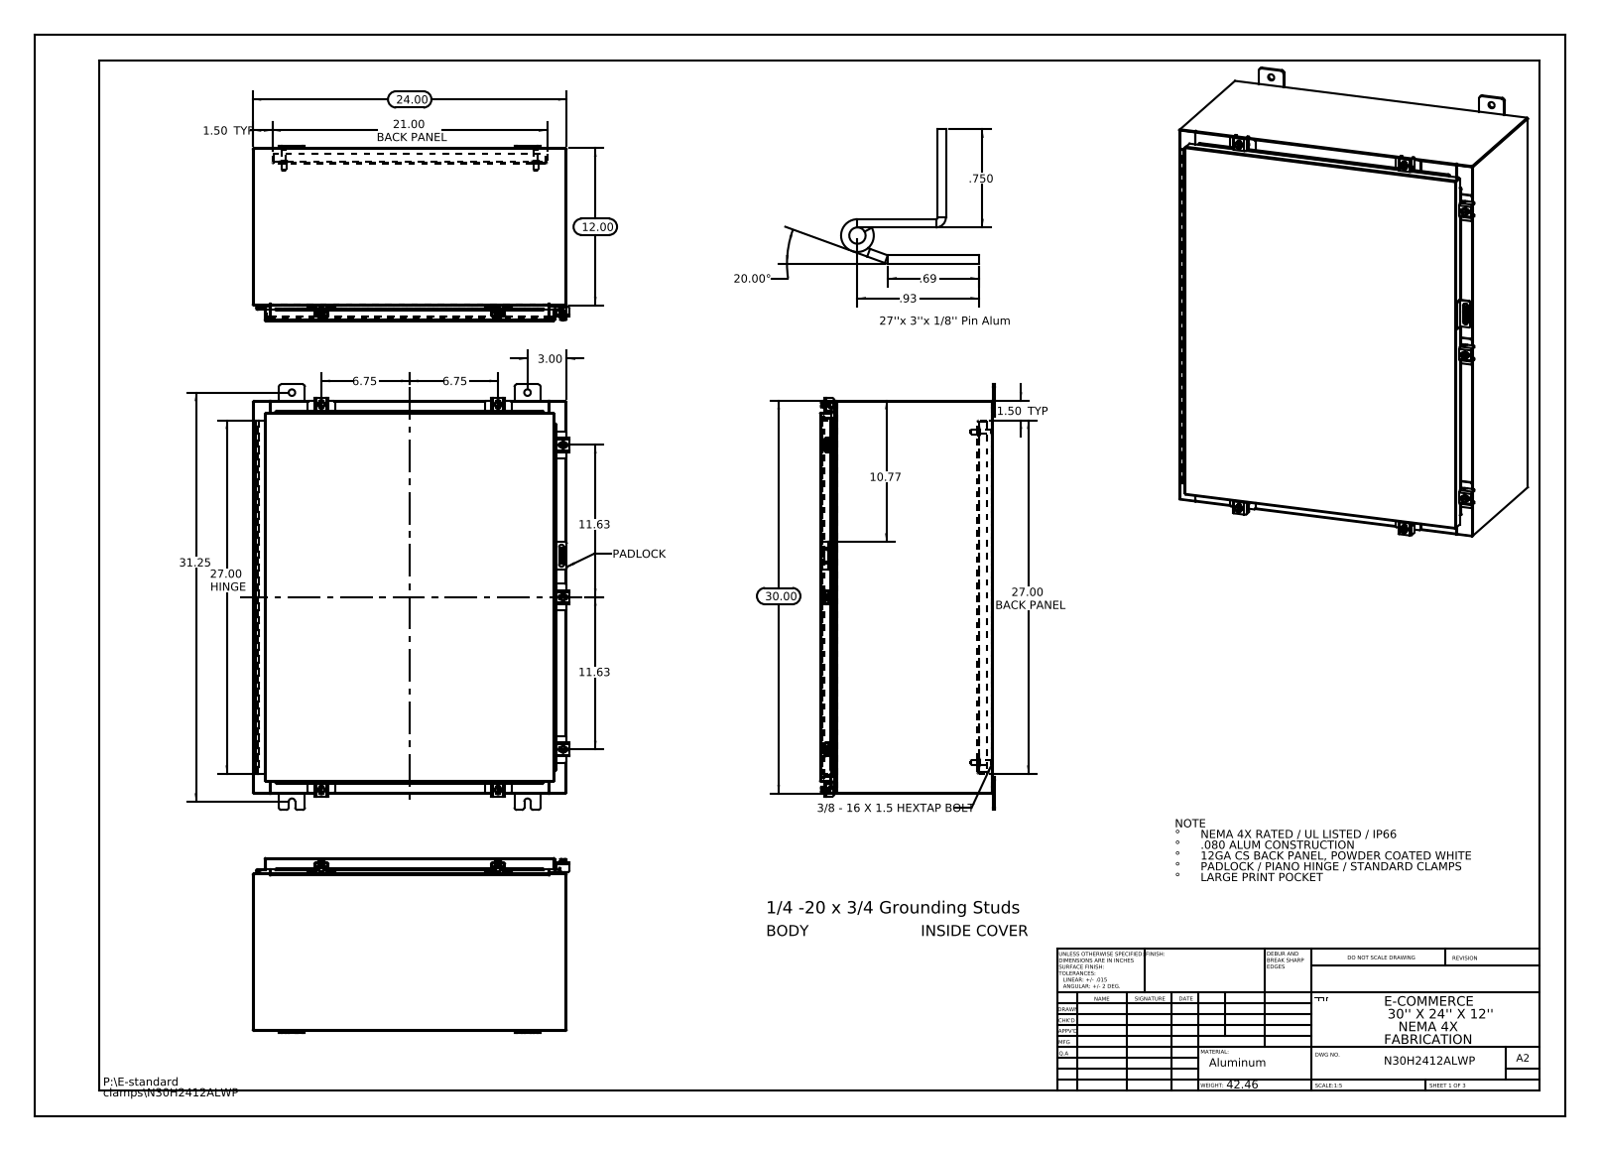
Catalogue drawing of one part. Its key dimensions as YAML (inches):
part_name: "N30H2412ALWP Hinge Cover Side; N30H2412ALWP Clamp Top; N30H2412ALWP Mounting Studs; N30H2412ALWP Padlock Hasp (+8 more)"
step_written_by: "SolidWorks 2013 (CONFIG_CONTROL_DESIGN)"
units: inches
bodies: {solids: 52, faces: 1990, planar: 1056, cylindrical: 830, other: 104}
overall_size: [32.5, 24.211, 13.389]
volume: 296.9
surface_area: 7480
round_holes:
  - {diameter: 0.5, count: 8}
  - {diameter: 0.213, count: 7}
  - {diameter: 0.26, count: 7}
  - {diameter: 0.125, count: 2}
  - {diameter: 0.125, count: 1}
round_bosses_or_shafts:
  - {diameter: 0.25, count: 8}
  - {diameter: 0.5, count: 7}
  - {diameter: 0.399, count: 7}
  - {diameter: 0.625, count: 4}
  - {diameter: 0.375, count: 4}
  - {diameter: 0.33, count: 4}
partial_cylinders:
  - {radius: 0.06, count: 34}
  - {radius: 0.013, count: 27}
  - {radius: 0.19, count: 24}
  - {radius: 0.088, count: 21}
  - {radius: 0.12, count: 14}
  - {radius: 0.141, count: 14}
  - {radius: 0.05, count: 11}
  - {radius: 0.08, count: 10}
face_to_face_distances: [0.075, 13.126, 23.925, 13.201, 13.051, 0.104, 1, 29.925, 1.075, 12.051]
hole_center_spacings: [27.501, 31.878, 1.858, 2.277, 2.326, 2.423, 3.561, 3.561]
